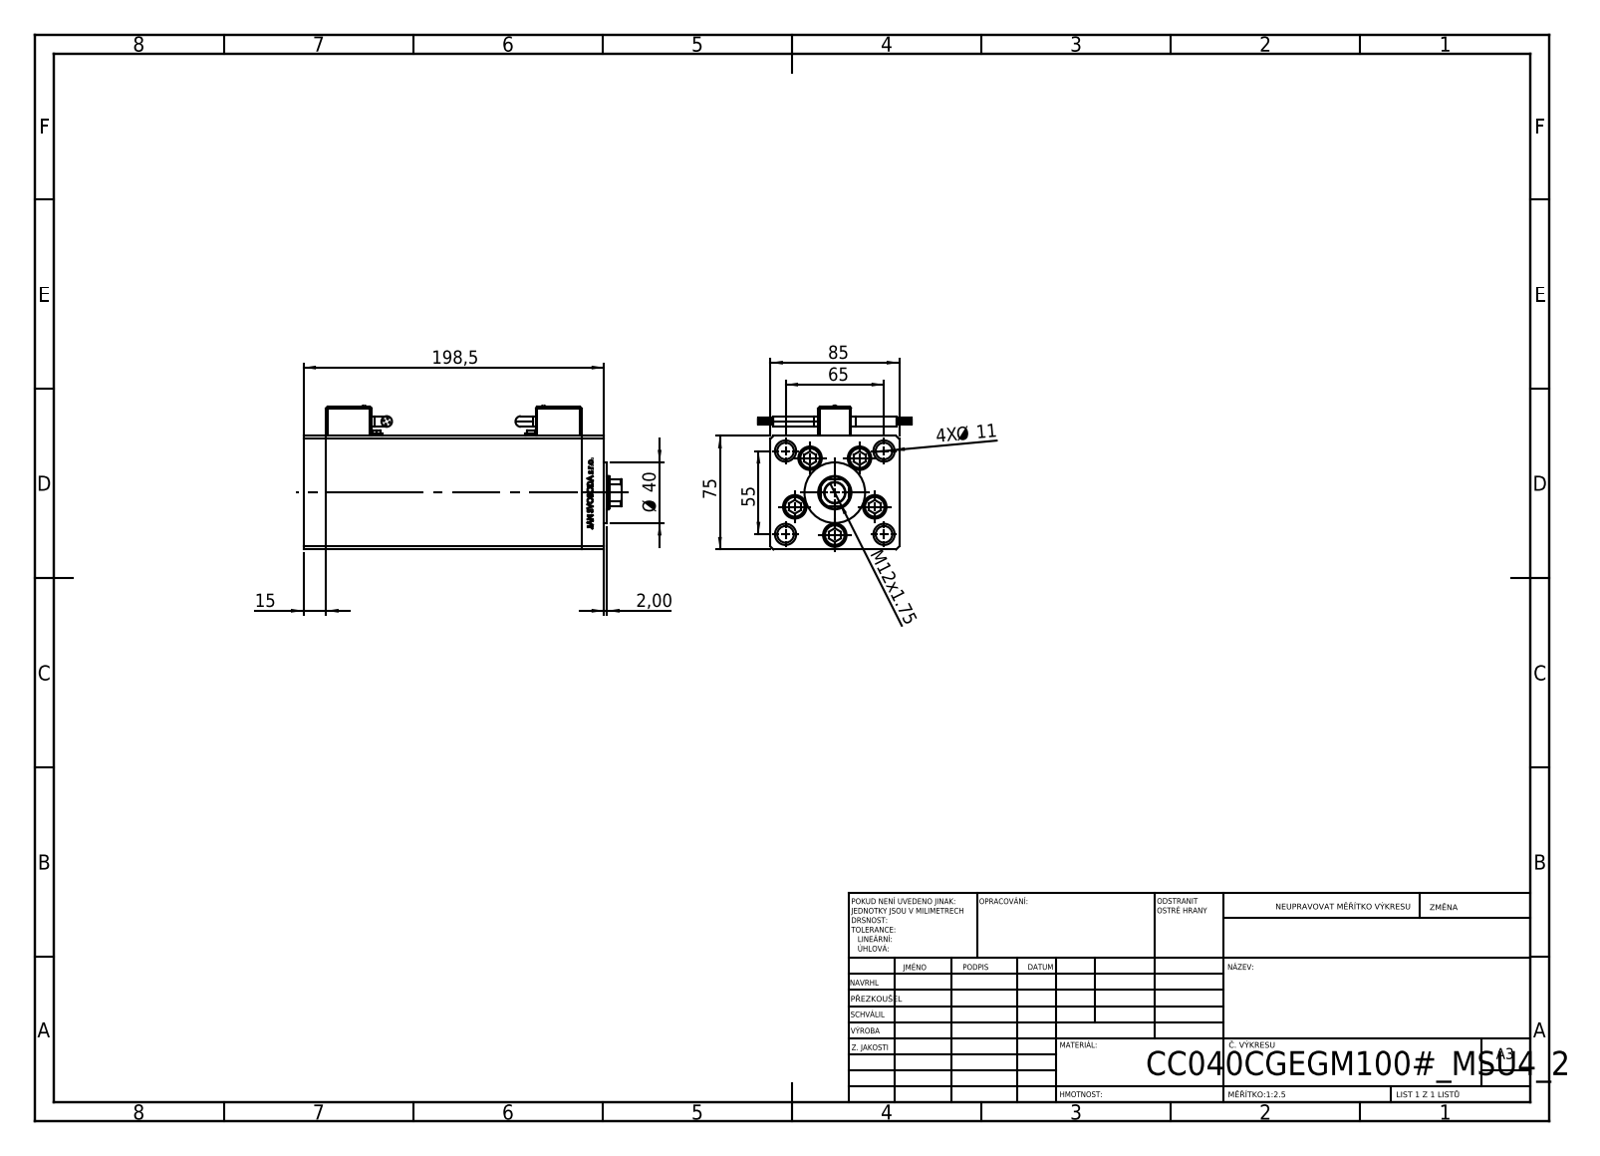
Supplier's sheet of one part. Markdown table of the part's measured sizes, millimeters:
| quantity | value |
| --- | --- |
| part name | ALLEN BOLT; Magnetic_Switch_MSU4; V220C_C MIDDLE; V220C FRONT (+2 more) |
| STEP written by | SolidWorks 2019 (CONFIG_CONTROL_DESIGN) |
| units | millimeters |
| bodies | 15 solids, 1367 faces (620 planar, 249 cylindrical, 498 other) |
| overall size | 210 × 101.6 × 95.1 |
| volume | 1 087 000 mm³ |
| surface area | 204 172 mm² |
| round holes (diameter × count) | 11 × 9, 15.5 × 5, 10 × 4, 14 × 4, 3.6 × 2, 5 × 2, 7 × 2, 13.5 × 1, 14.5 × 1, 22 × 1 |
| round bosses / shafts (diameter × count) | 0.85 × 8, 8 × 5, 14.5 × 4, 7 × 4, 6 × 2, 3.5 × 2, 2.5 × 2, 40 × 1 |
| partial cylindrical surfaces (radius × count) | 1 × 24, 4 × 4, 0.93 × 2, 10.5 × 1 |
| main face-to-face distances | 85, 75, 168.5, 15, 183.5, 10.5, 68.5, 198.5, 34.25, 6.5 |
| hole center spacings | 28, 42.57, 8.25, 16.86, 19.17, 32.33, 32.5, 33.63 |
